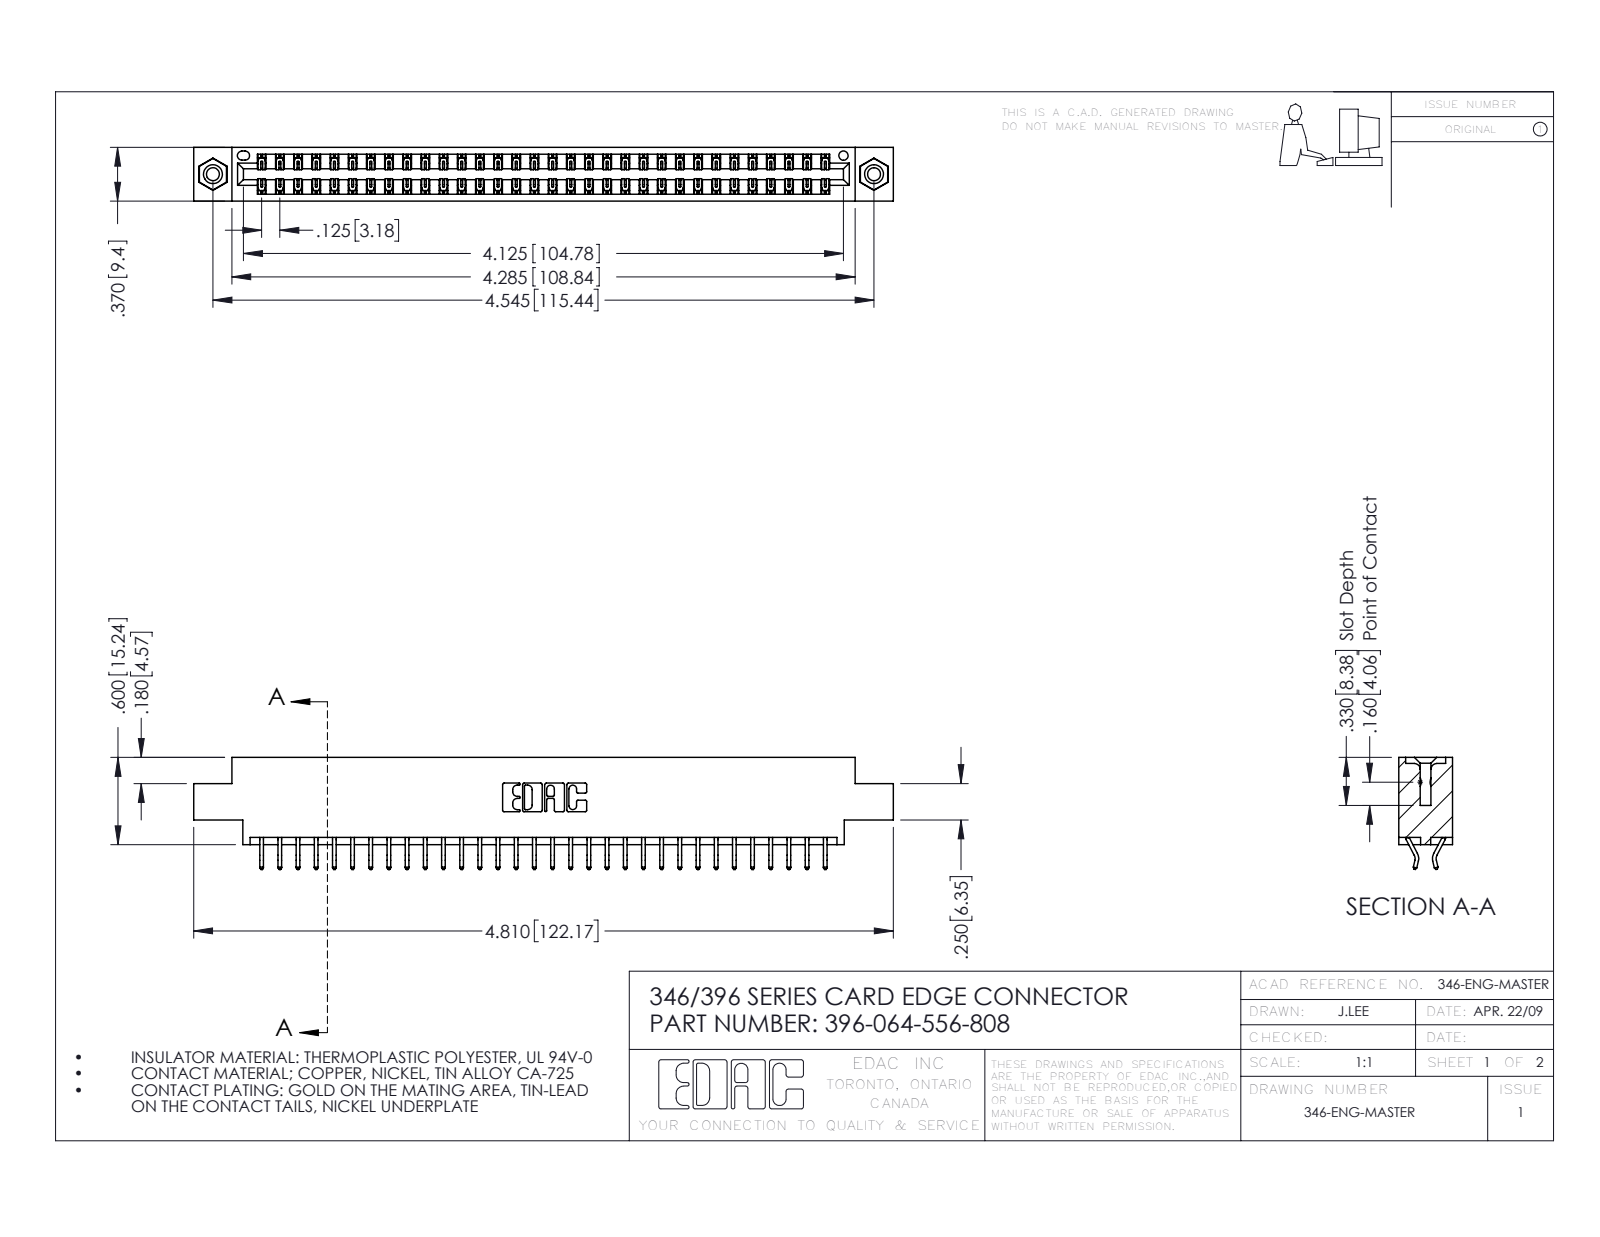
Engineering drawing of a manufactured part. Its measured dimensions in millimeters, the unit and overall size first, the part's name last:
Units: millimetres
Overall size (bounding box): 122.2 × 19.6 × 9.4
Round holes (diameter × count): ⌀2.3 ×2, ⌀3.2 ×2, ⌀4 ×2, ⌀1.6 ×1
Round bosses / shafts (diameter × count): ⌀3.9 ×2
Partial cylindrical surfaces — rounded edges, fillets, slot ends (radius × count): R0.2 ×96, R0.3 ×22, R0.2 ×6, R0.8 ×6, R0.7 ×3, R0.3 ×2, R0.4 ×2, R0.6 ×2
Main face-to-face distances: 1.2, 8.2, 9.4, 6.4, 0.6, 1.8, 7.6, 7, 5.6, 3.8
Hole centre spacings: 6.2, 110.2, 115.4
Volume: 11 700 mm³ · Surface area: 16 030 mm²
Bodies: 67 solids, 3898 faces (2608 planar, 1274 cylindrical, 16 other)
Part name (STEP PRODUCT): 396-064-556-808; 345-292-001_556 Tail; 345-250-001_345-250-003-102; 346 Part_0.170 Offset - 0.156 Dia-TI
STEP written by: SolidWorks 2016 (CONFIG_CONTROL_DESIGN)
